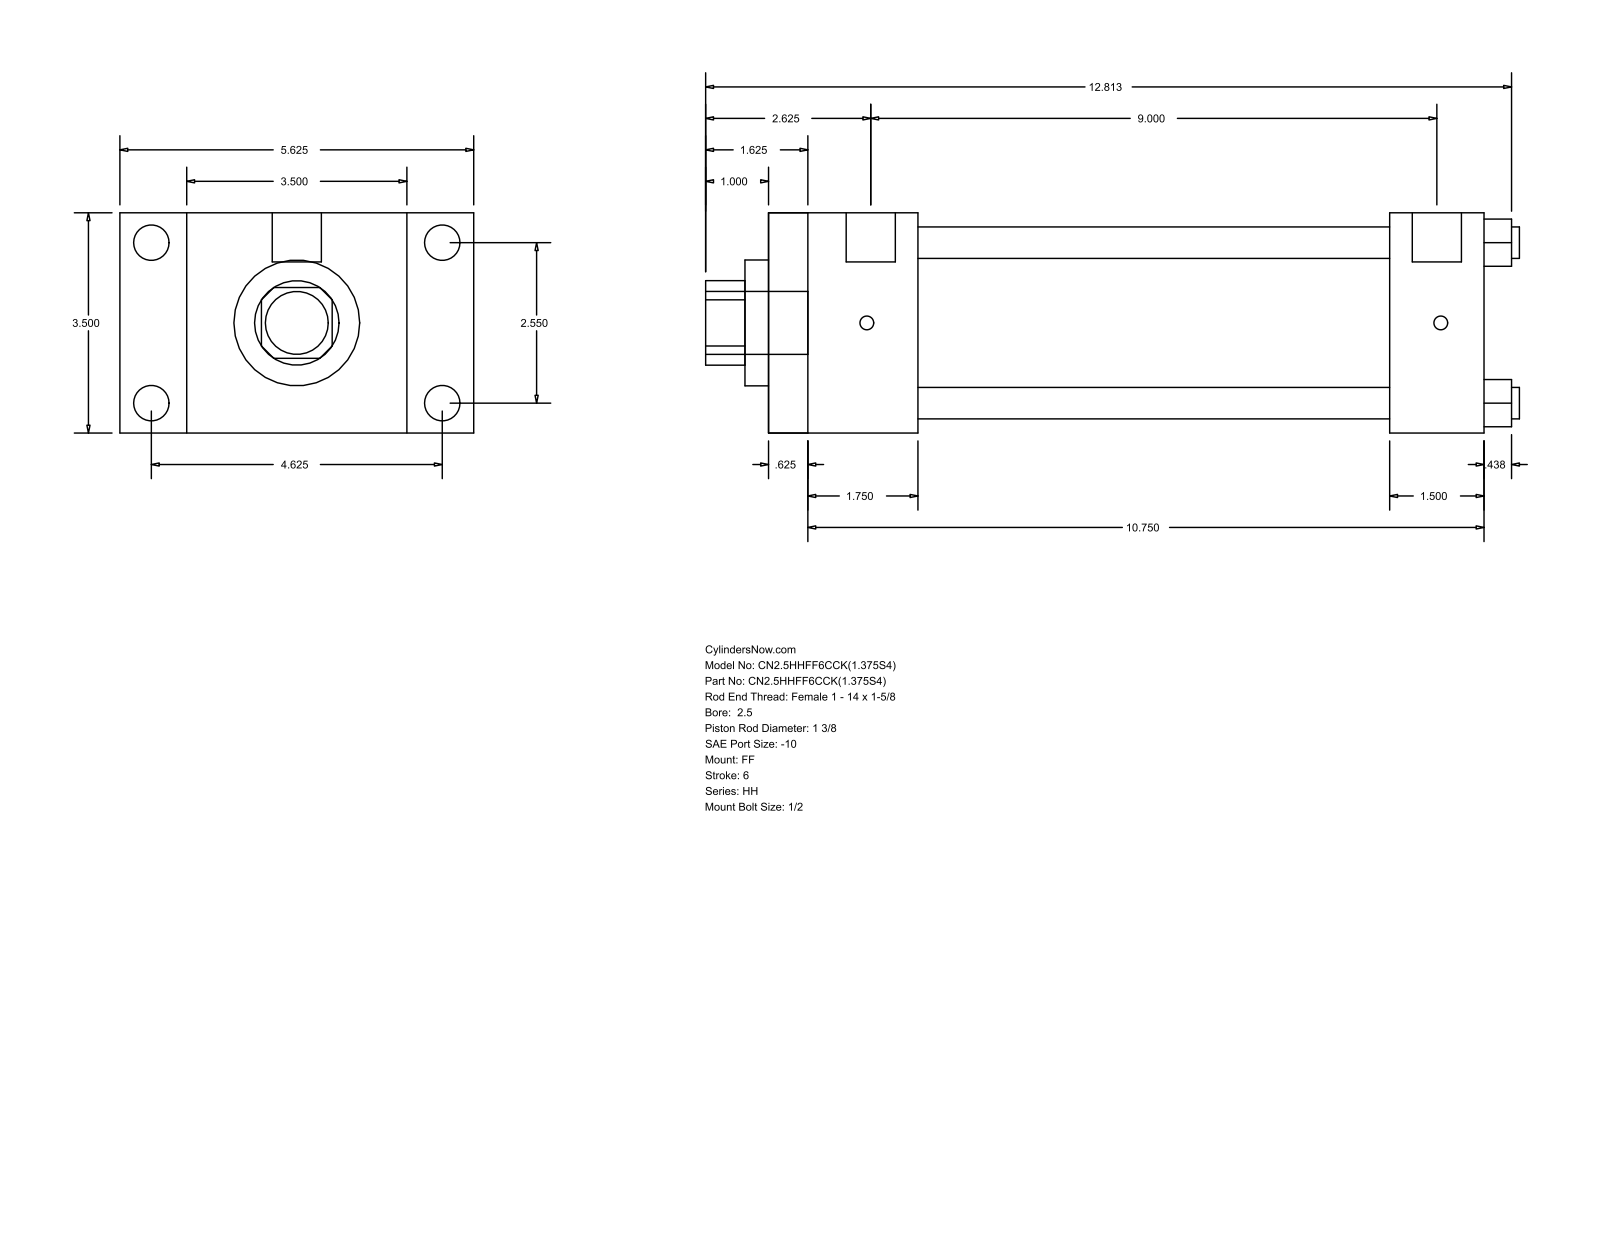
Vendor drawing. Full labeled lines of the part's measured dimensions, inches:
Part name (STEP PRODUCT): HH_FF__0250_1.375
STEP written by: GSSL Pune (CONFIG_CONTROL_DESIGN)
Units: inches
Bodies: 0 solids, 92 faces (64 planar, 28 cylindrical, 0 other)
Overall size (bounding box): 12.937 × 5.625 × 3.5
Round holes (diameter × count): ⌀0.5 ×4, ⌀1.375 ×1, ⌀2 ×1, ⌀2.875 ×1
Round bosses / shafts (diameter × count): ⌀0.563 ×4, ⌀0.219 ×4, ⌀0.781 ×2, ⌀1 ×1
Partial cylindrical surfaces — rounded edges, fillets, slot ends (radius × count): R0.672 ×1
Main face-to-face distances: 3.5, 11.375, 0.625, 10.75, 2.375, 1.75, 9, 9.875, 9.25, 7.5
Hole centre spacings: 1.803, 2.55, 3.606
